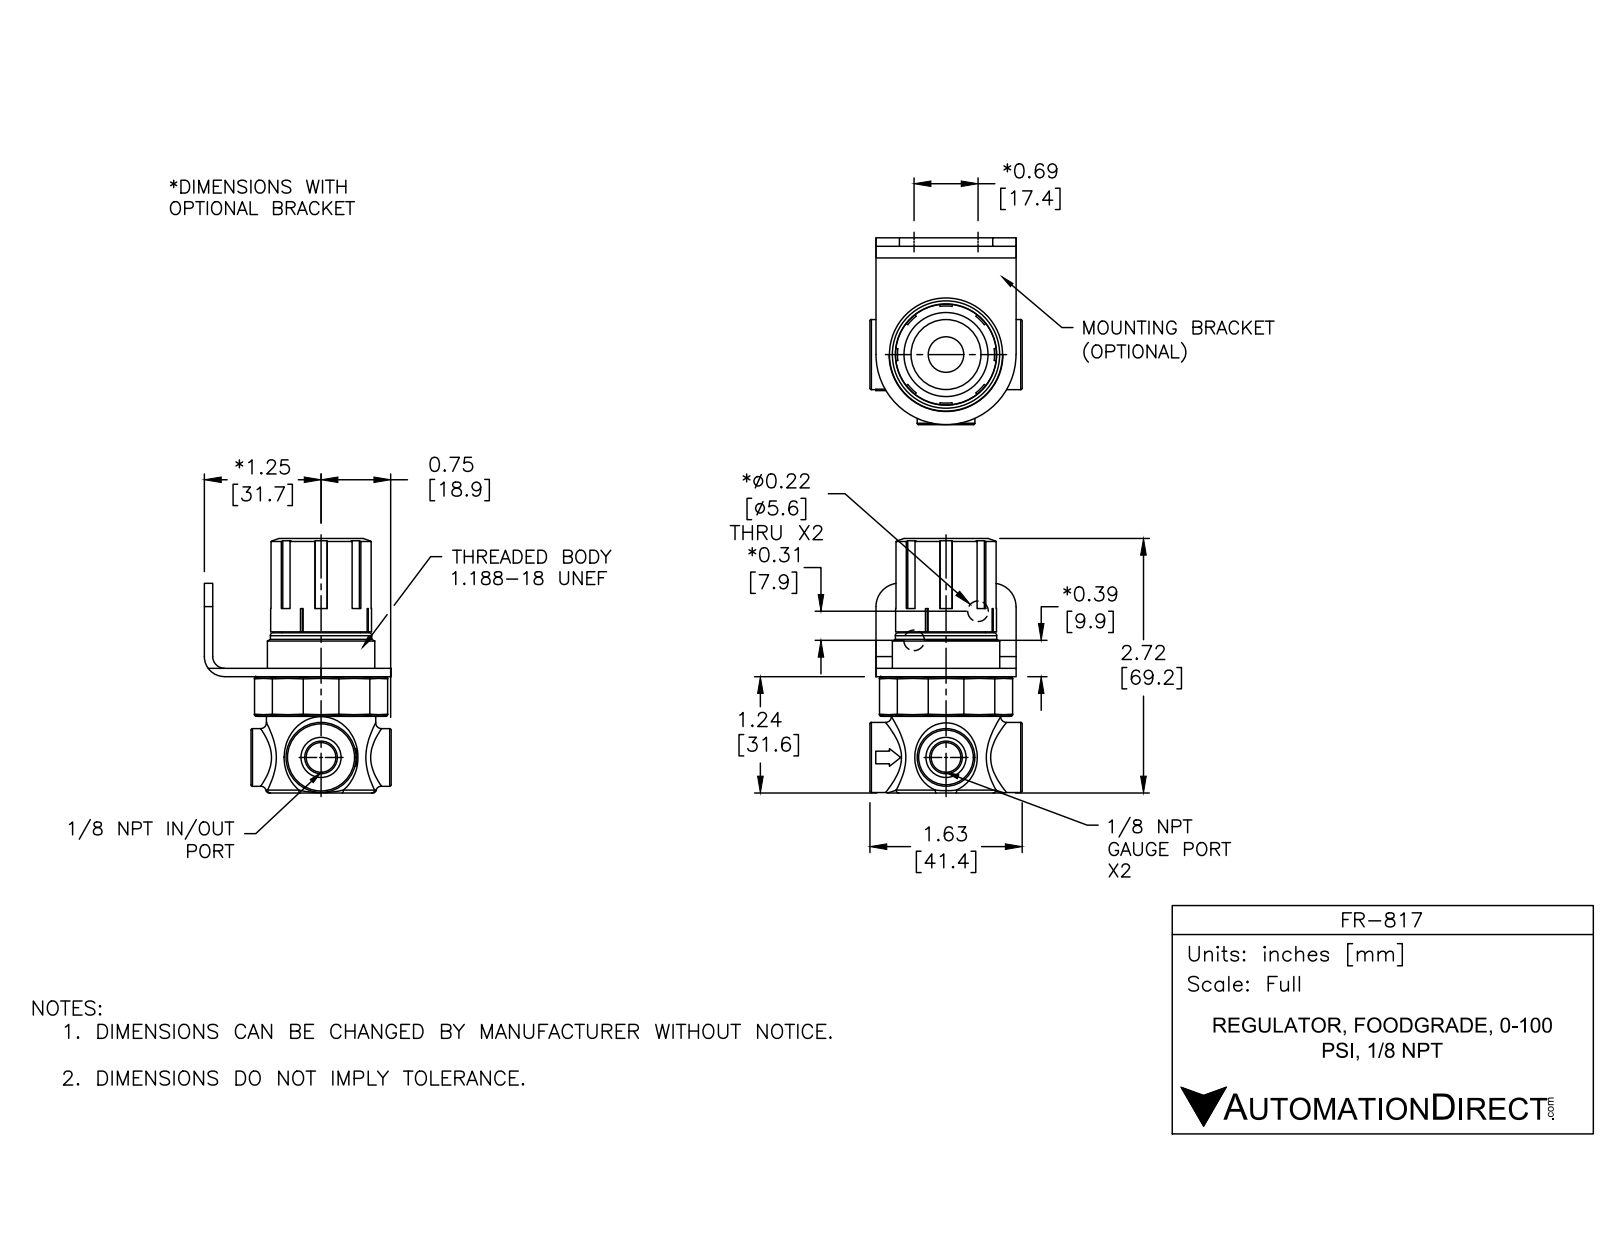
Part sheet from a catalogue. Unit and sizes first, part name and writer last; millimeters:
Units: millimetres
Overall size (bounding box): 69.2 × 41.4 × 38.1
Round holes (diameter × count): ⌀8.4 ×2, ⌀19.1 ×1, ⌀21.3 ×1
Round bosses / shafts (diameter × count): ⌀29.7 ×1, ⌀29.2 ×1, ⌀27.6 ×1, ⌀19.1 ×1, ⌀15.7 ×1, ⌀9.7 ×1
Partial cylindrical surfaces — rounded edges, fillets, slot ends (radius × count): R0.5 ×24, R13.2 ×1, R13.7 ×1
Main face-to-face distances: 10.8, 12.1, 1.3, 25.9, 15.1, 13.8, 36.9, 20.8, 31.6, 32.9
Volume: 51 620 mm³ · Surface area: 16 490 mm²
Bodies: 5 solids, 178 faces (66 planar, 73 cylindrical, 39 other)
Part name (STEP PRODUCT): FR-817
STEP written by: SolidWorks 2015 (CONFIG_CONTROL_DESIGN)
